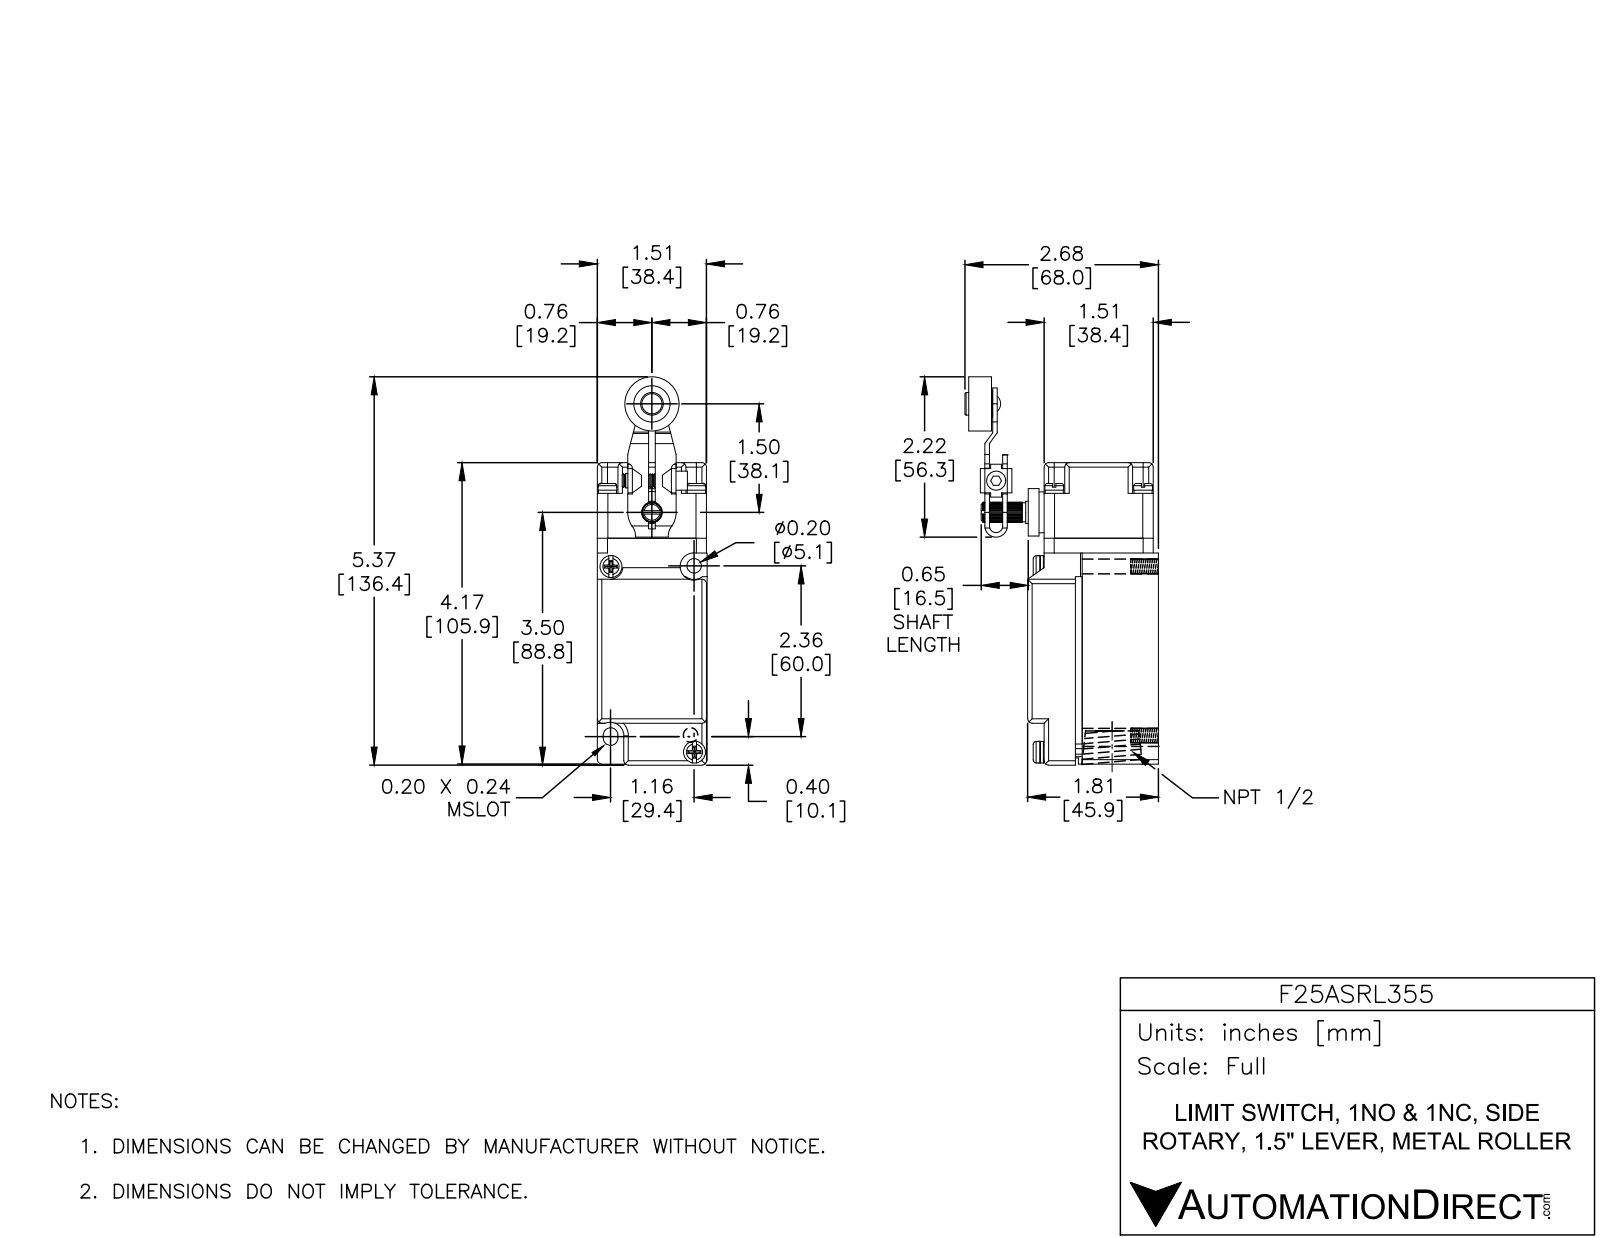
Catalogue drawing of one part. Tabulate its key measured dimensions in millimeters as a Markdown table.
| quantity | value |
| --- | --- |
| part name | Imported107; Imported108; Imported111; Imported110 (+8 more) |
| STEP written by | SolidWorks 2002296 (CONFIG_CONTROL_DESIGN) |
| units | millimeters |
| bodies | 17 solids, 929 faces (513 planar, 235 cylindrical, 181 other) |
| overall size | 136.4 × 68 × 38.6 |
| volume | 169 600 mm³ |
| surface area | 47 590 mm² |
| round holes (diameter × count) | 4.5 × 4, 4.8 × 3, 5.1 × 3, 4 × 1, 4.3 × 1, 6.4 × 1, 6.4 × 1, 12.7 × 1, 14.7 × 1 |
| round bosses / shafts (diameter × count) | 6.6 × 4, 6.4 × 4, 7.7 × 2, 7.6 × 2, 19.1 × 1, 16.6 × 1, 14.4 × 1, 9.5 × 1 |
| partial cylindrical surfaces (radius × count) | 1.6 × 29, 0.8 × 16, 0.4 × 8, 3.7 × 8, 1.6 × 4, 3.6 × 4, 0.8 × 3, 0.6 × 2 |
| main face-to-face distances | 2.4, 29.2, 26.8, 38.6, 16.8, 19.2, 45.9, 38.4, 5.8, 11 |
| hole center spacings | 31.2, 31.2, 44.2, 71.5, 5.7, 6, 23.8, 23.9 |
